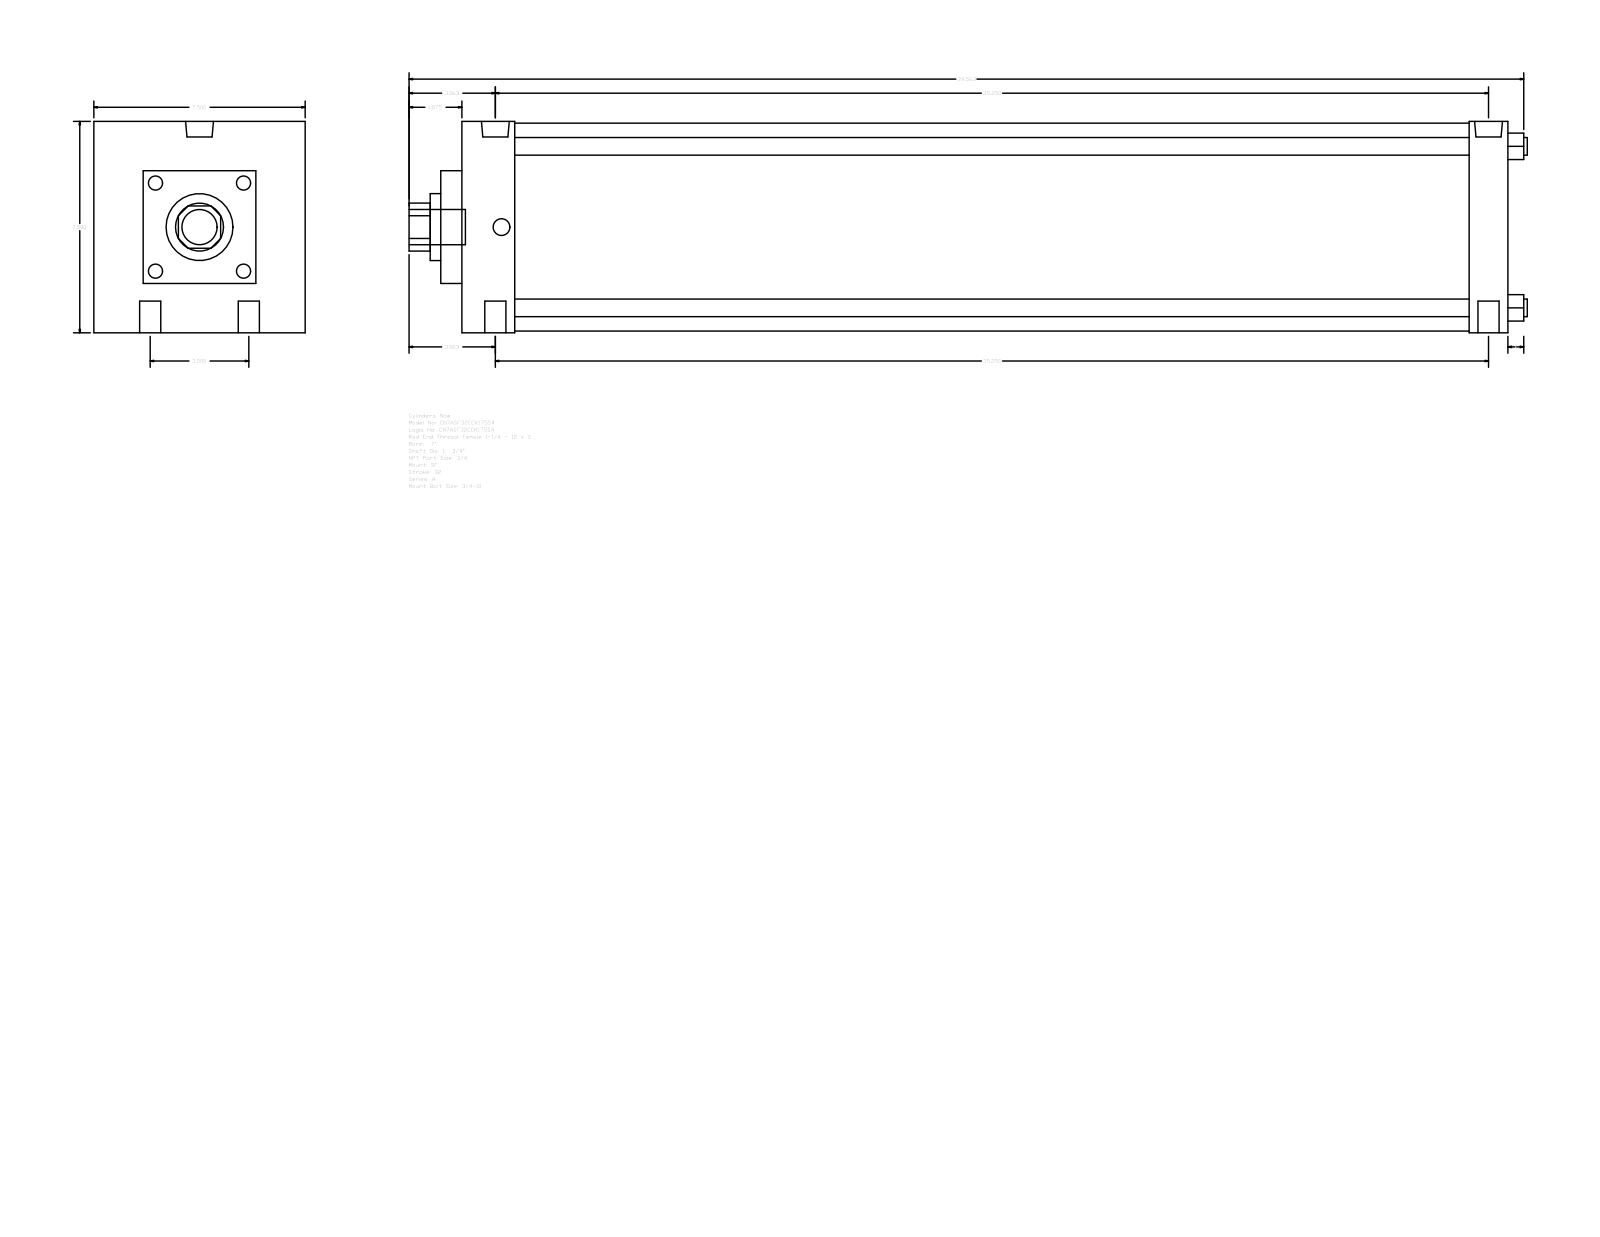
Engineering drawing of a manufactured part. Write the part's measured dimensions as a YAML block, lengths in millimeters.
part_name: "A_SF__0700_1.75"
step_written_by: "GSSL Pune (CONFIG_CONTROL_DESIGN)"
units: millimeters
bodies: {solids: 0, faces: 93, planar: 67, cylindrical: 26, other: 0}
overall_size: [1008.06, 190.5, 190.5]
round_holes:
  - {diameter: 19.05, count: 4}
  - {diameter: 15.08, count: 2}
  - {diameter: 25.12, count: 2}
  - {diameter: 44.45, count: 1}
  - {diameter: 60.33, count: 1}
round_bosses_or_shafts:
  - {diameter: 15.88, count: 4}
  - {diameter: 187.32, count: 1}
  - {diameter: 31.75, count: 1}
partial_cylinders:
  - {radius: 21.63, count: 1}
face_to_face_distances: [190.5, 942.98, 44.45, 19.05, 47.63, 908.05, 860.42, 895.35, 34.93, 146.05]
hole_center_spacings: [44.45, 896.45, 895.35, 88.9, 899.75, 884.23]
